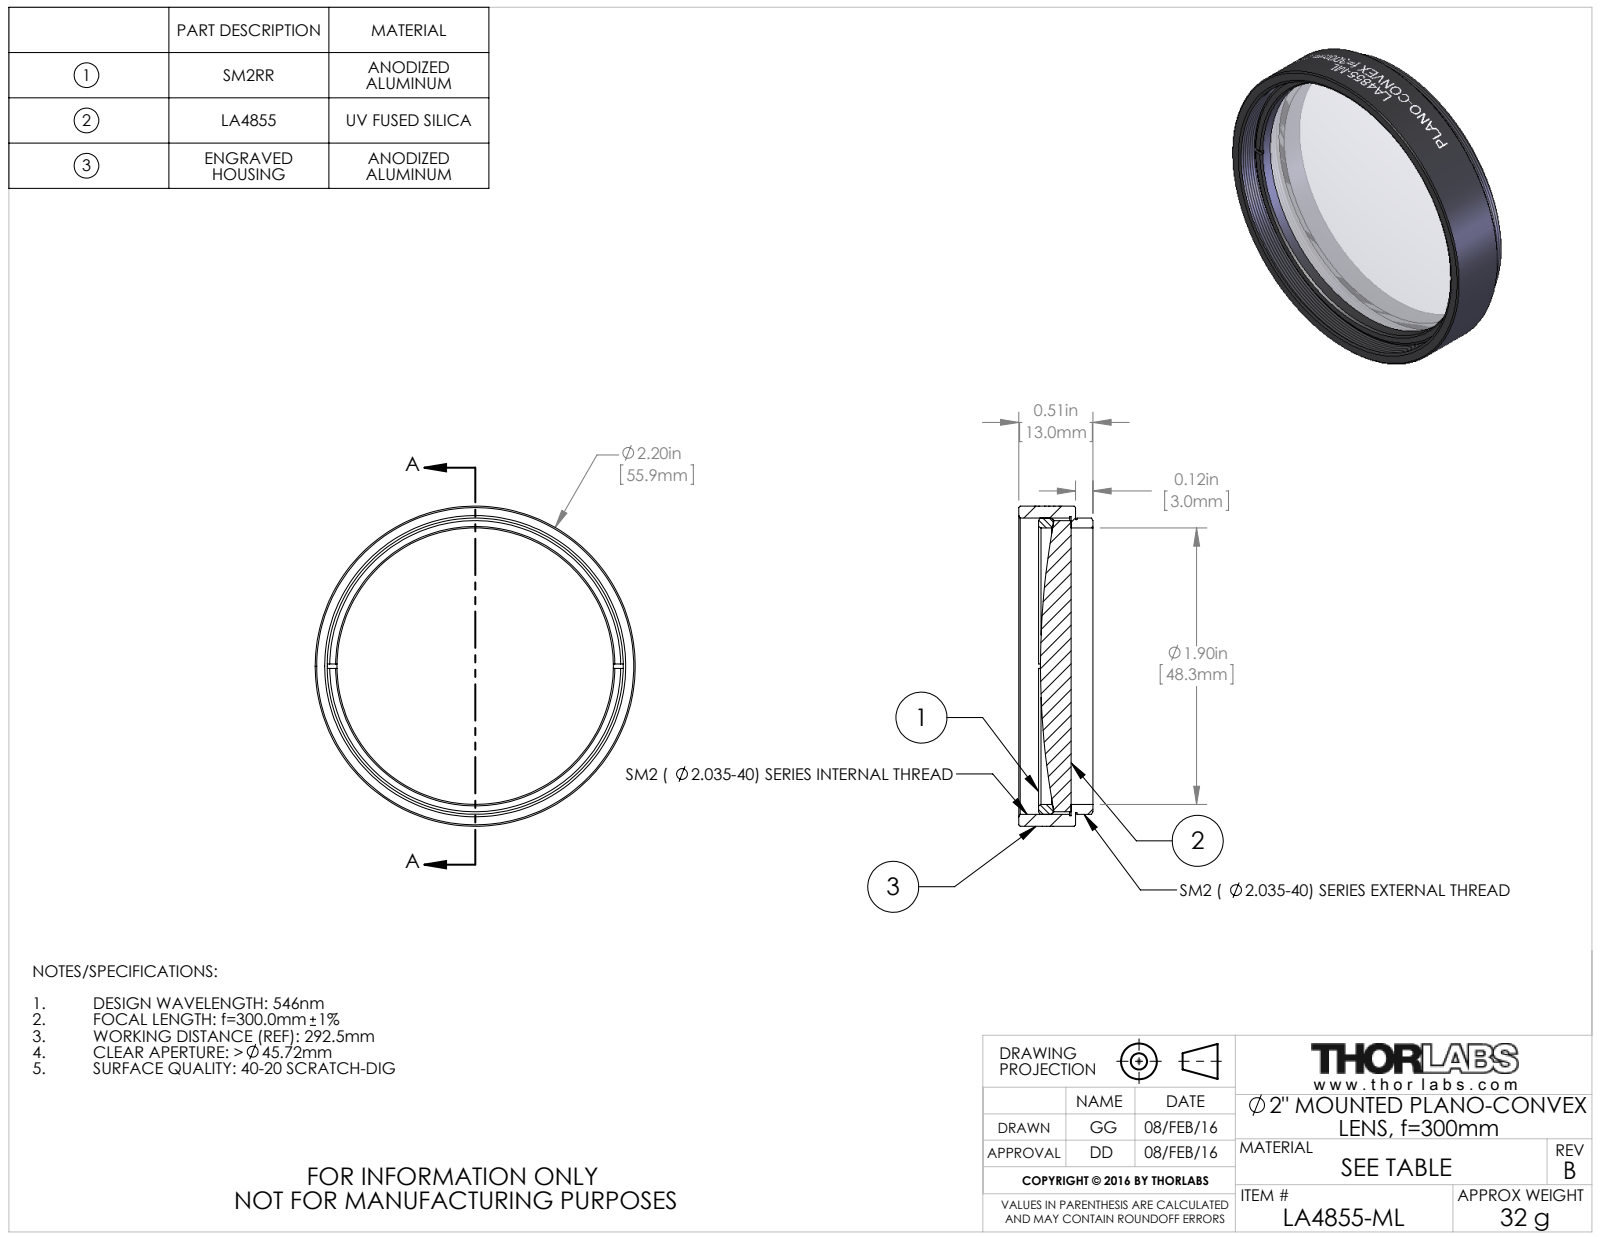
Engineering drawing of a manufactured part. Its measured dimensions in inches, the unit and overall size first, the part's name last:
Units: inches
Overall size (bounding box): 2.2 × 2.2 × 0.51
Round holes (diameter × count): ⌀1.9 ×1, ⌀2.055 ×1
Round bosses / shafts (diameter × count): ⌀2.2 ×1, ⌀2.035 ×1, ⌀2.015 ×1, ⌀2 ×1
Main face-to-face distances: 0.03, 0.39, 0.36, 0.12, 0.15, 0.51, 0.274, 0.154, 0.124, 0.236
Volume: 0.83 in³ · Surface area: 17.62 in²
Bodies: 3 solids, 110 faces (16 planar, 74 cylindrical, 20 other)
Part name (STEP PRODUCT): TTN039404-E0W
STEP written by: SolidWorks 2014 (CONFIG_CONTROL_DESIGN)
